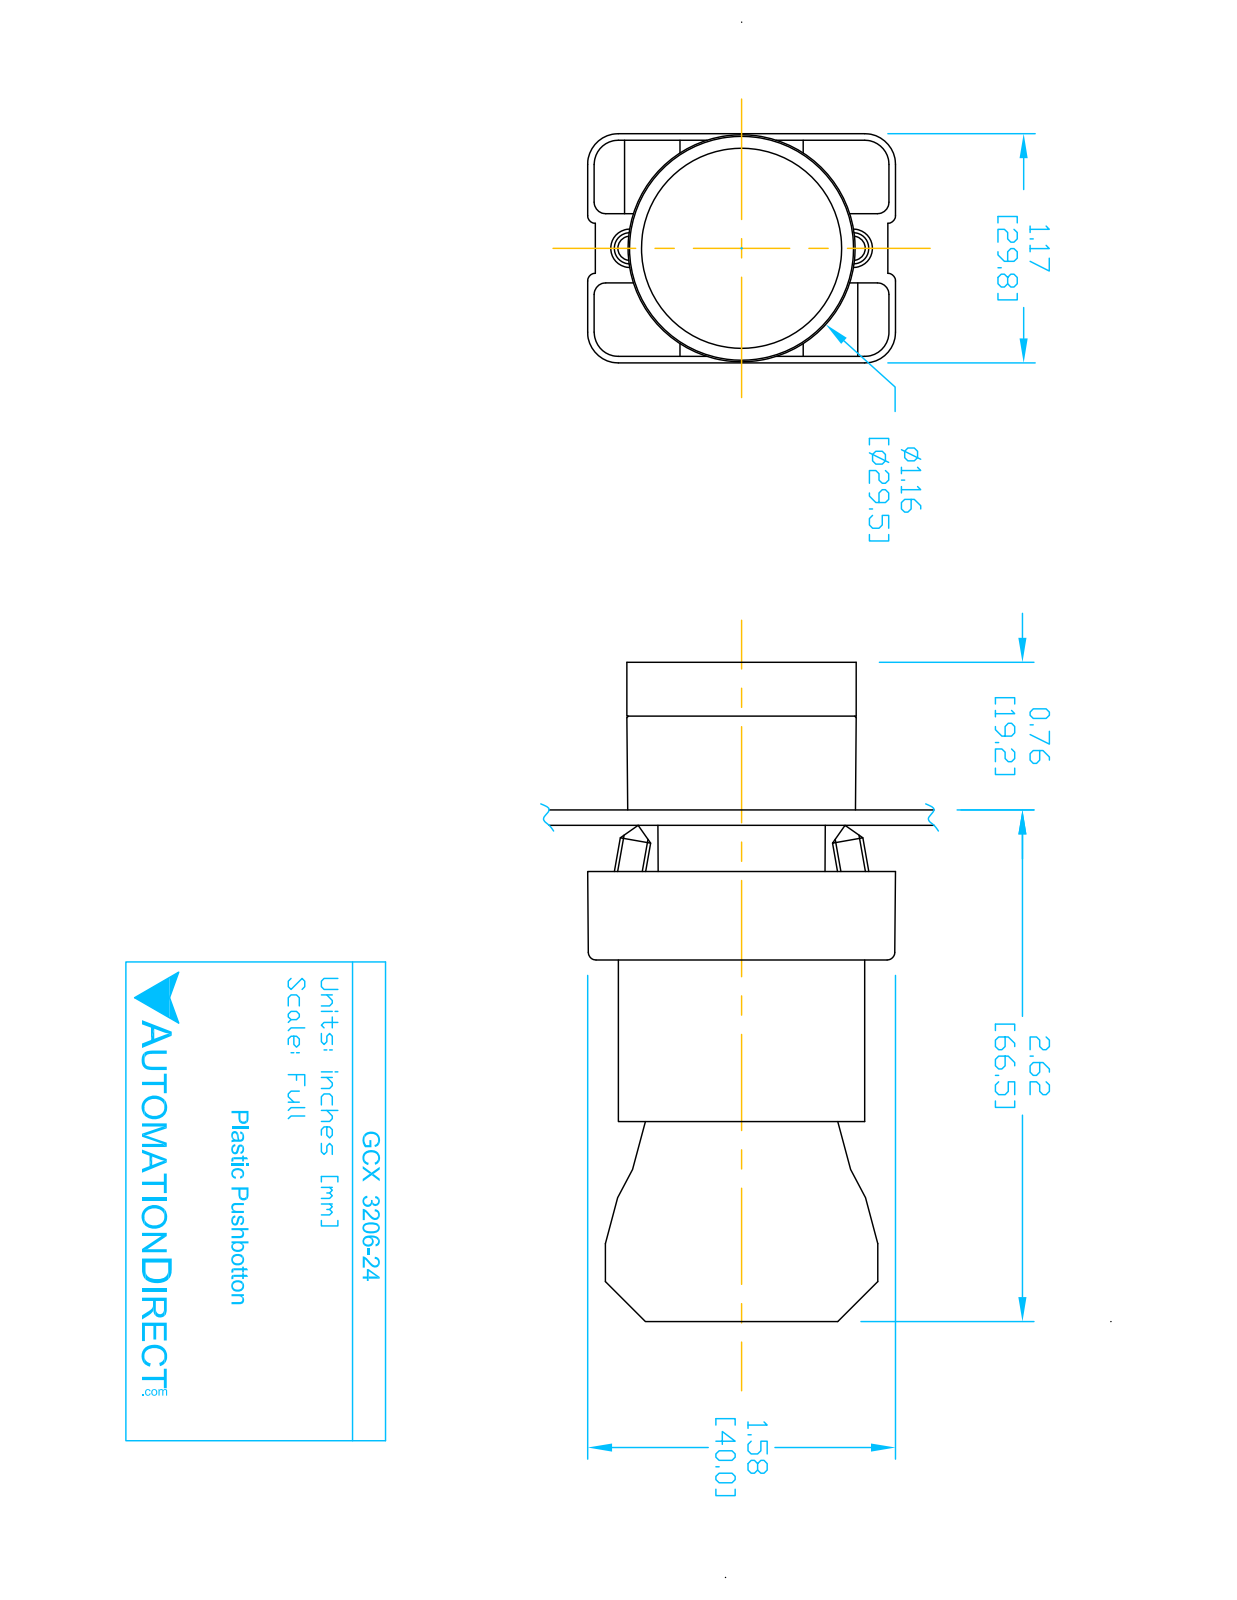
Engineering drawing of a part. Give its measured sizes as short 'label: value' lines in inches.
name: ecx1040; ECX1050; GCX3206-24; GCX3206 OPERATOR (+1 more)
written by: SolidWorks 2016 (AUTOMOTIVE_DESIGN)
unit: in
bodies: 8 solids, 431 faces (252 planar, 148 cylindrical, 31 other)
size: 3.319 × 1.581 × 1.177
volume: 2.794 in³; area: 38.77 in²
holes: 2× ⌀0.079, 2× ⌀0.124, 2× ⌀0.13, 1× ⌀0.087, 1× ⌀0.197, 1× ⌀0.469, 1× ⌀0.878, 1× ⌀0.888, 1× ⌀1.024
bosses: 4× ⌀0.157, 1× ⌀1.175, 1× ⌀1.004, 1× ⌀0.945, 1× ⌀0.856, 1× ⌀0.78, 1× ⌀0.504
rounds: 24× R0.059, 12× R0.041, 12× R0.124, 12× R0.157, 8× R0.039, 2× R0.128, 1× R0.02, 1× R0.063
face distances: 0.827, 0.579, 2.02, 1.193, 1.171, 0.276, 2.295, 1.469, 0.031, 0.033
hole spacings: 0.236, 0.544, 0.472, 0.49
